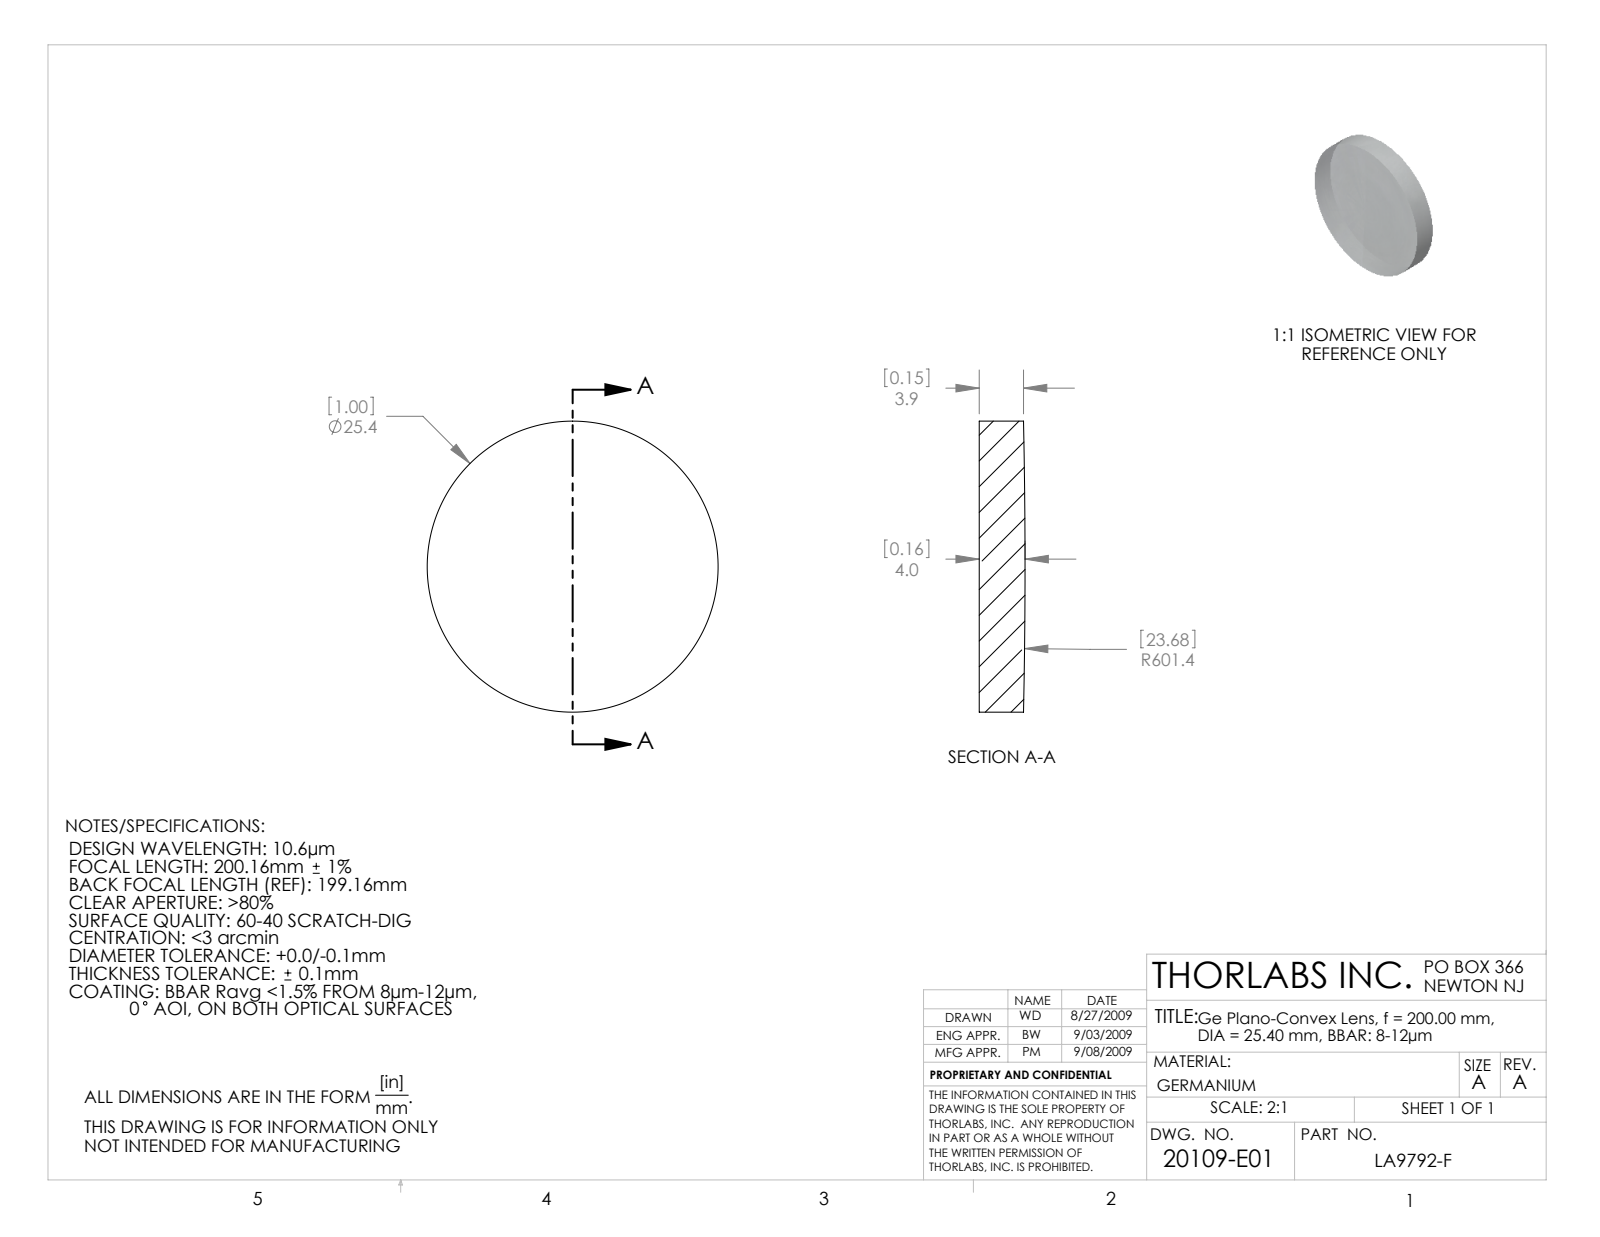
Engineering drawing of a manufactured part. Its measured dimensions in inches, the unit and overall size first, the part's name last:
Units: inches
Overall size (bounding box): 1 × 1 × 0.157
Round bosses / shafts (diameter × count): ⌀1 ×1
Volume: 0.122 in³ · Surface area: 2.049 in²
Bodies: 1 solid, 5 faces (1 planar, 2 cylindrical, 2 other)
Part name (STEP PRODUCT): 20109-E0W
STEP written by: SolidWorks 2007 (CONFIG_CONTROL_DESIGN)
